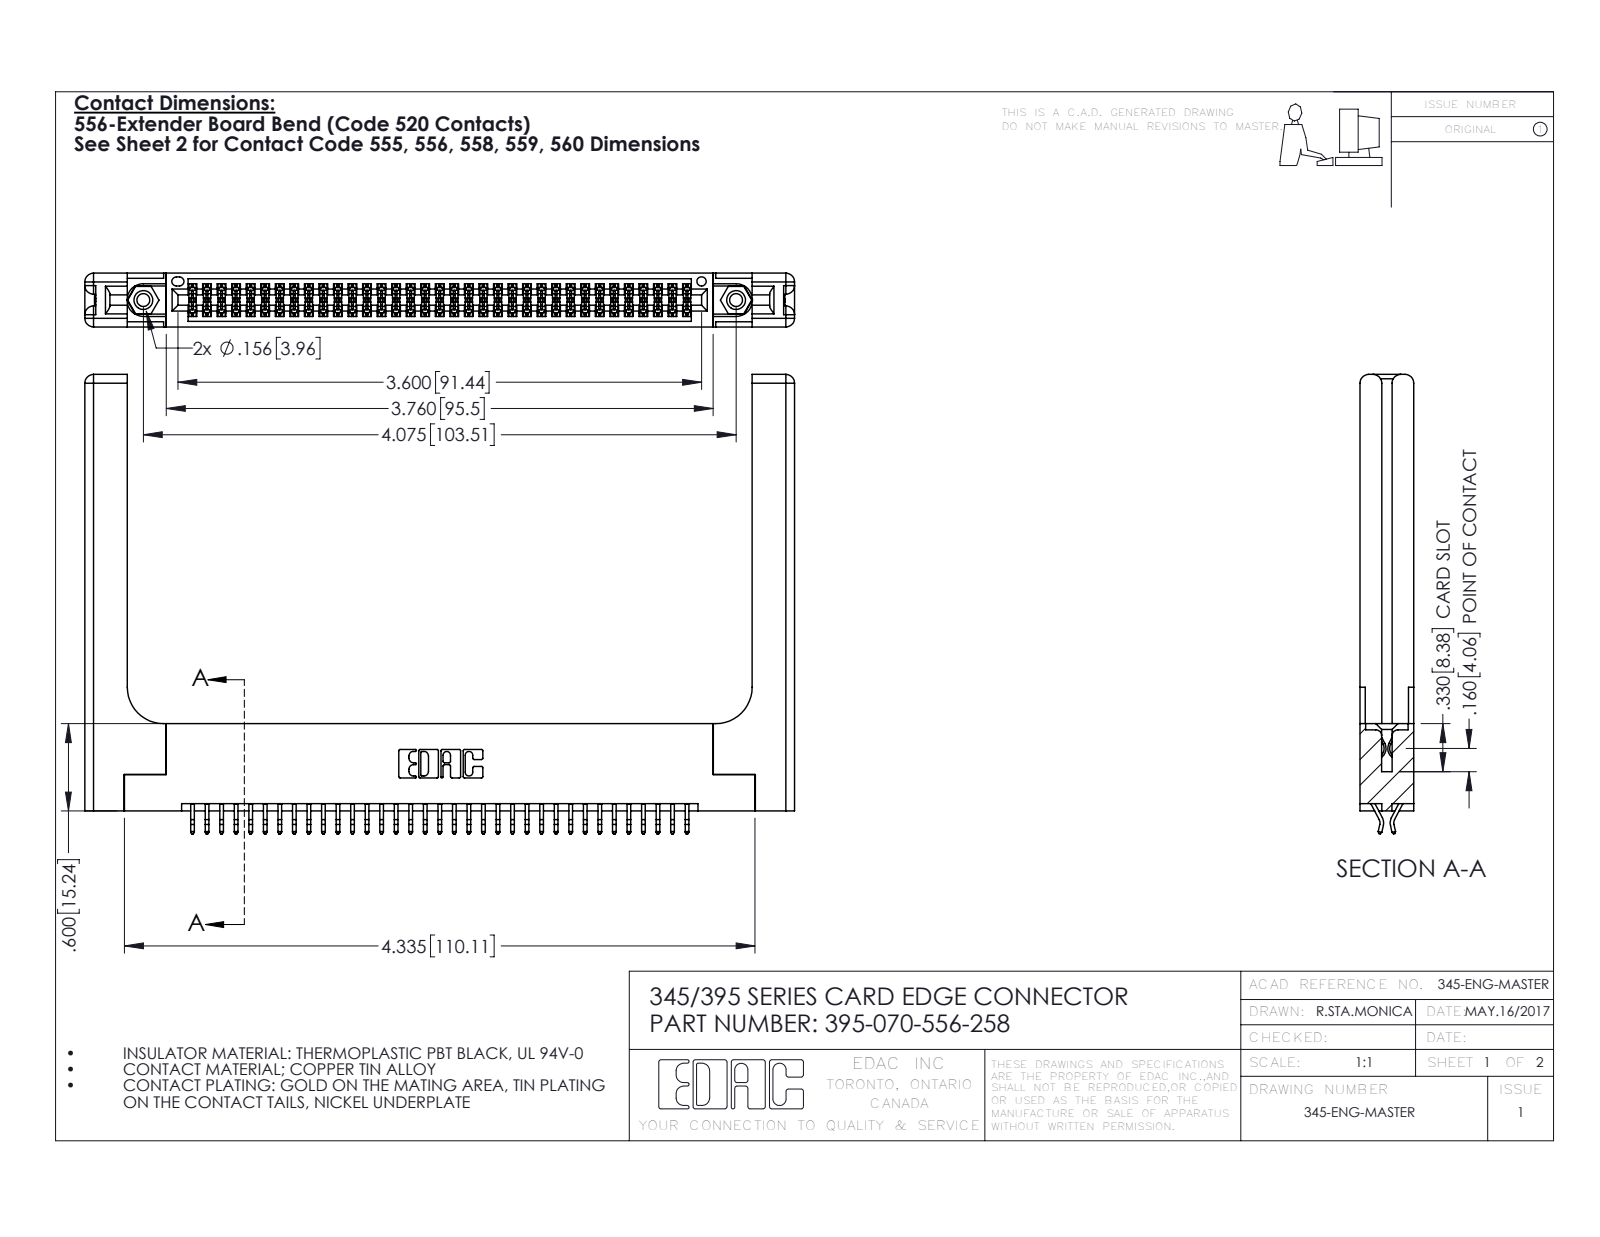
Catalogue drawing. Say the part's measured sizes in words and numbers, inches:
The part is named "345-250-001_345-250-001-102; 345-292-001_556 Tail; 345-220-058_345-220-058; 395-070-556-258 (+1 more)". Its 3-D file was written by "SolidWorks 2016 (CONFIG_CONTROL_DESIGN)". It is 75 solids with 4302 faces: 2818 planar, 1424 cylindrical and 60 other. Overall it measures 4.879 by 3.157 by 0.37 inches. Its volume is 1.248 cubic inches and its surface area 34.96 square inches. Round holes: 2 of diameter 0.089, 2 of diameter 0.125, 2 of diameter 0.156, 1 of diameter 0.064. Round bosses or shafts: 2 of diameter 0.155. Partial cylindrical surfaces (rounded edges, fillets, slot ends): 105 of radius 0.006, 22 of radius 0.01, 16 of radius 0.06, 6 of radius 0.007, 6 of radius 0.031, 3 of radius 0.026, 2 of radius 0.01, 2 of radius 0.014. The main face-to-face distances are 0.37, 0.072, 0.298, 0.2, 0.025, 0.098, 0.272, 0.225, 0.148, 0.15. The hole center spacings are 0.27, 3.839, 4.075.
